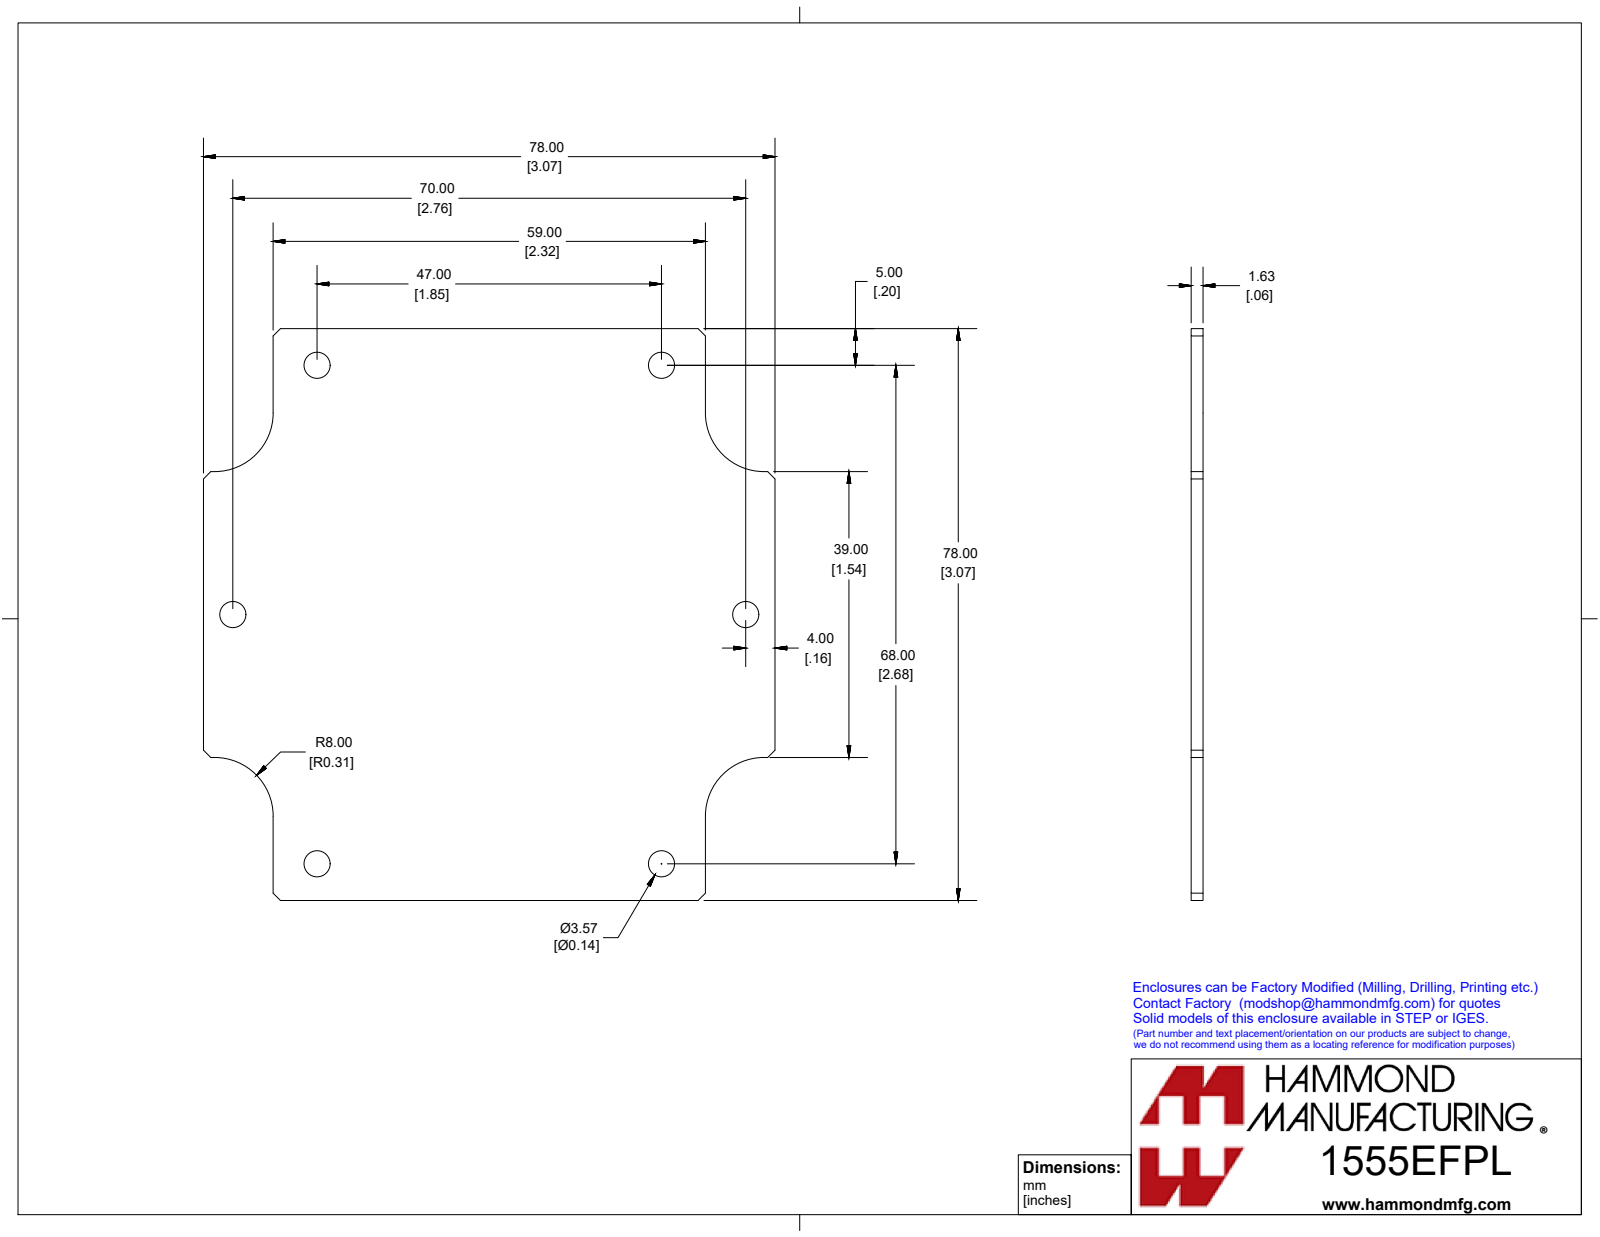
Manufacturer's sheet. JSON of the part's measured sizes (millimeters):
{"part_name": "1555EFPL", "step_written_by": "SolidWorks 2019 (CONFIG_CONTROL_DESIGN)", "units": "millimeters", "bodies": {"solids": 1, "faces": 32, "planar": 22, "cylindrical": 10, "other": 0}, "overall_size": [78, 78, 1.6], "volume_mm3": 8670, "surface_area_mm2": 11250, "round_holes": [[3.7, 6]], "partial_cylinders_radius": [[8, 4]], "face_to_face_distances": [1.6, 78, 9.5, 68.5, 59, 7.1, 88.4, 81.3, 95.4, 19.5], "hole_center_spacings": [35.9, 67.7, 47, 68, 82.7, 70]}
